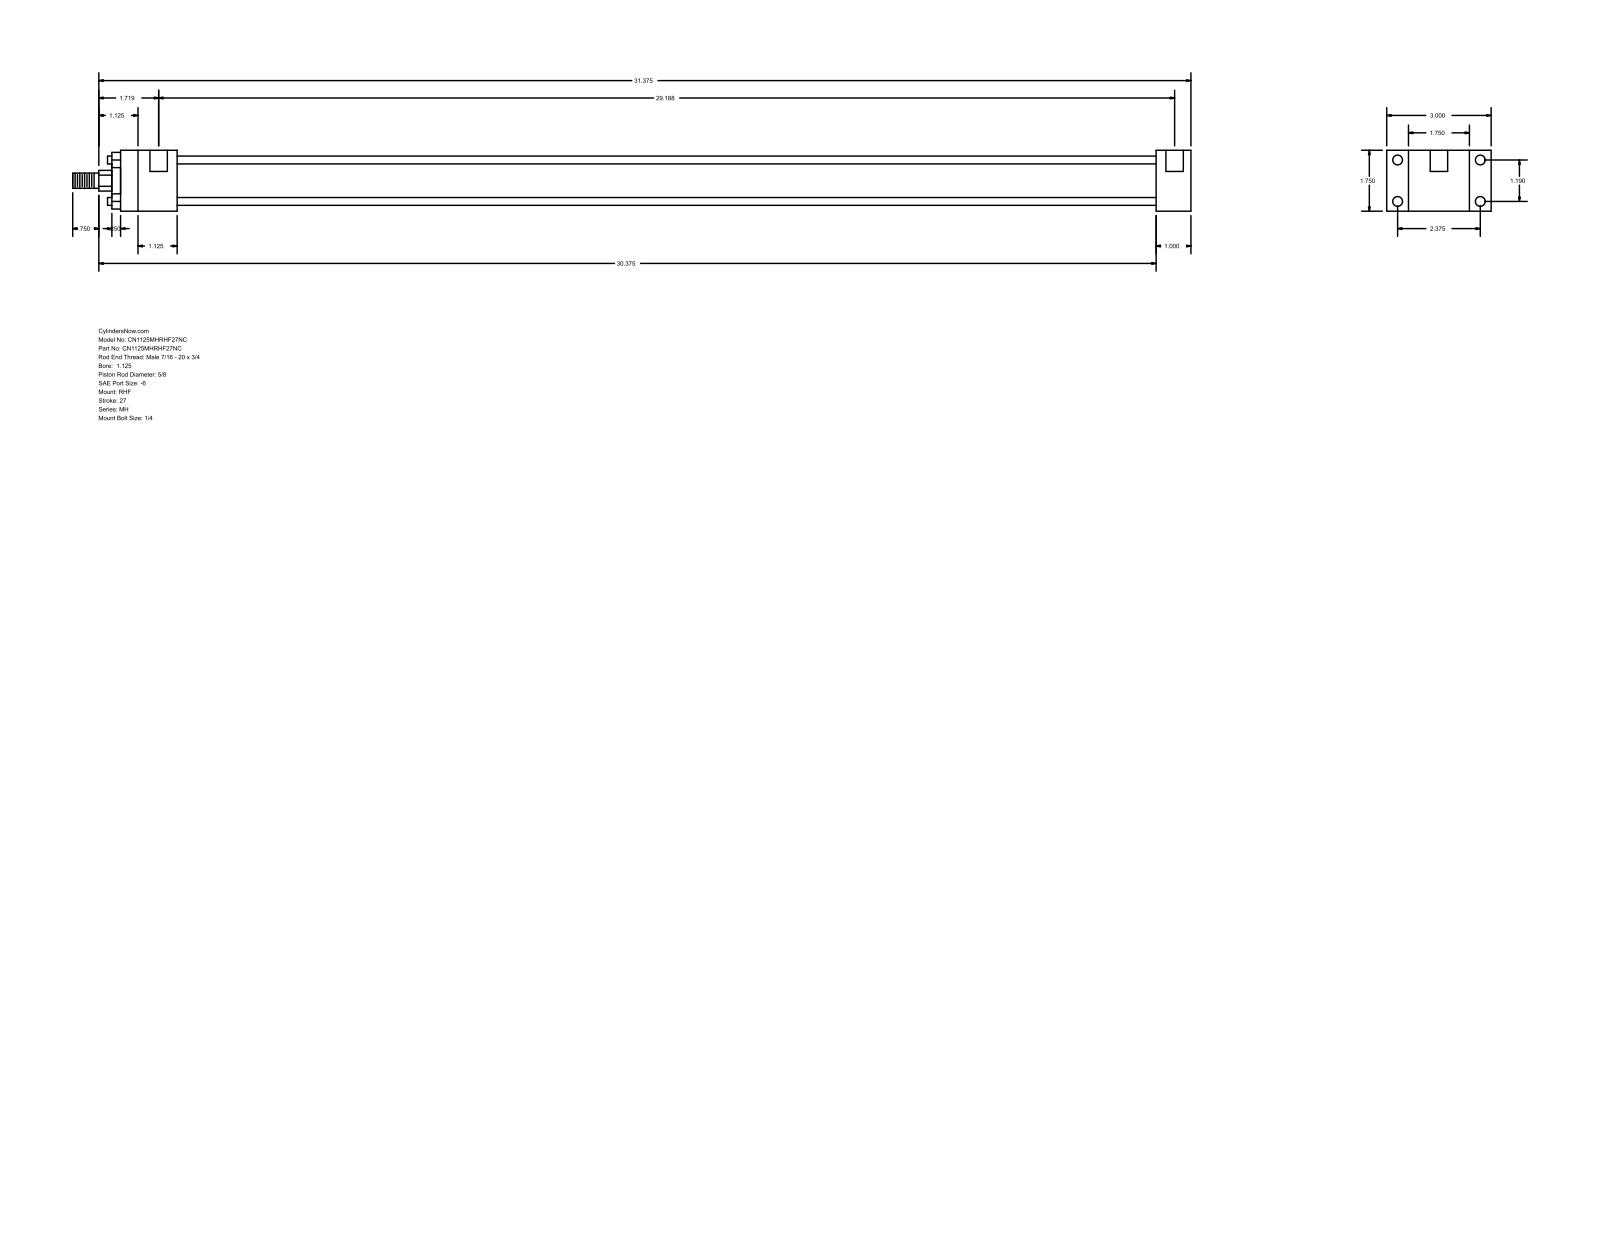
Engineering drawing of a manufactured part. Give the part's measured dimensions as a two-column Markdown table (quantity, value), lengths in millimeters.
| quantity | value |
| --- | --- |
| part name | MH_RHF__0112_0.625 |
| STEP written by | GSSL Pune (CONFIG_CONTROL_DESIGN) |
| units | millimeters |
| bodies | 0 solids, 88 faces (60 planar, 28 cylindrical, 0 other) |
| overall size | 815.98 × 76.2 × 44.45 |
| round holes (diameter × count) | 5.56 × 4, 7.14 × 4, 12.7 × 2 |
| round bosses / shafts (diameter × count) | 5.71 × 4, 34.92 × 1, 28.57 × 1, 15.88 × 1, 11.11 × 1 |
| partial cylindrical surfaces (radius × count) | 7.54 × 1 |
| main face-to-face distances | 44.46, 15.87, 25.4, 60.33, 76.2, 714.37, 739.77, 41.27, 755.64, 781.04 |
| hole center spacings | 30.22, 60.32, 67.47, 738.19, 3.17, 741.36 |
